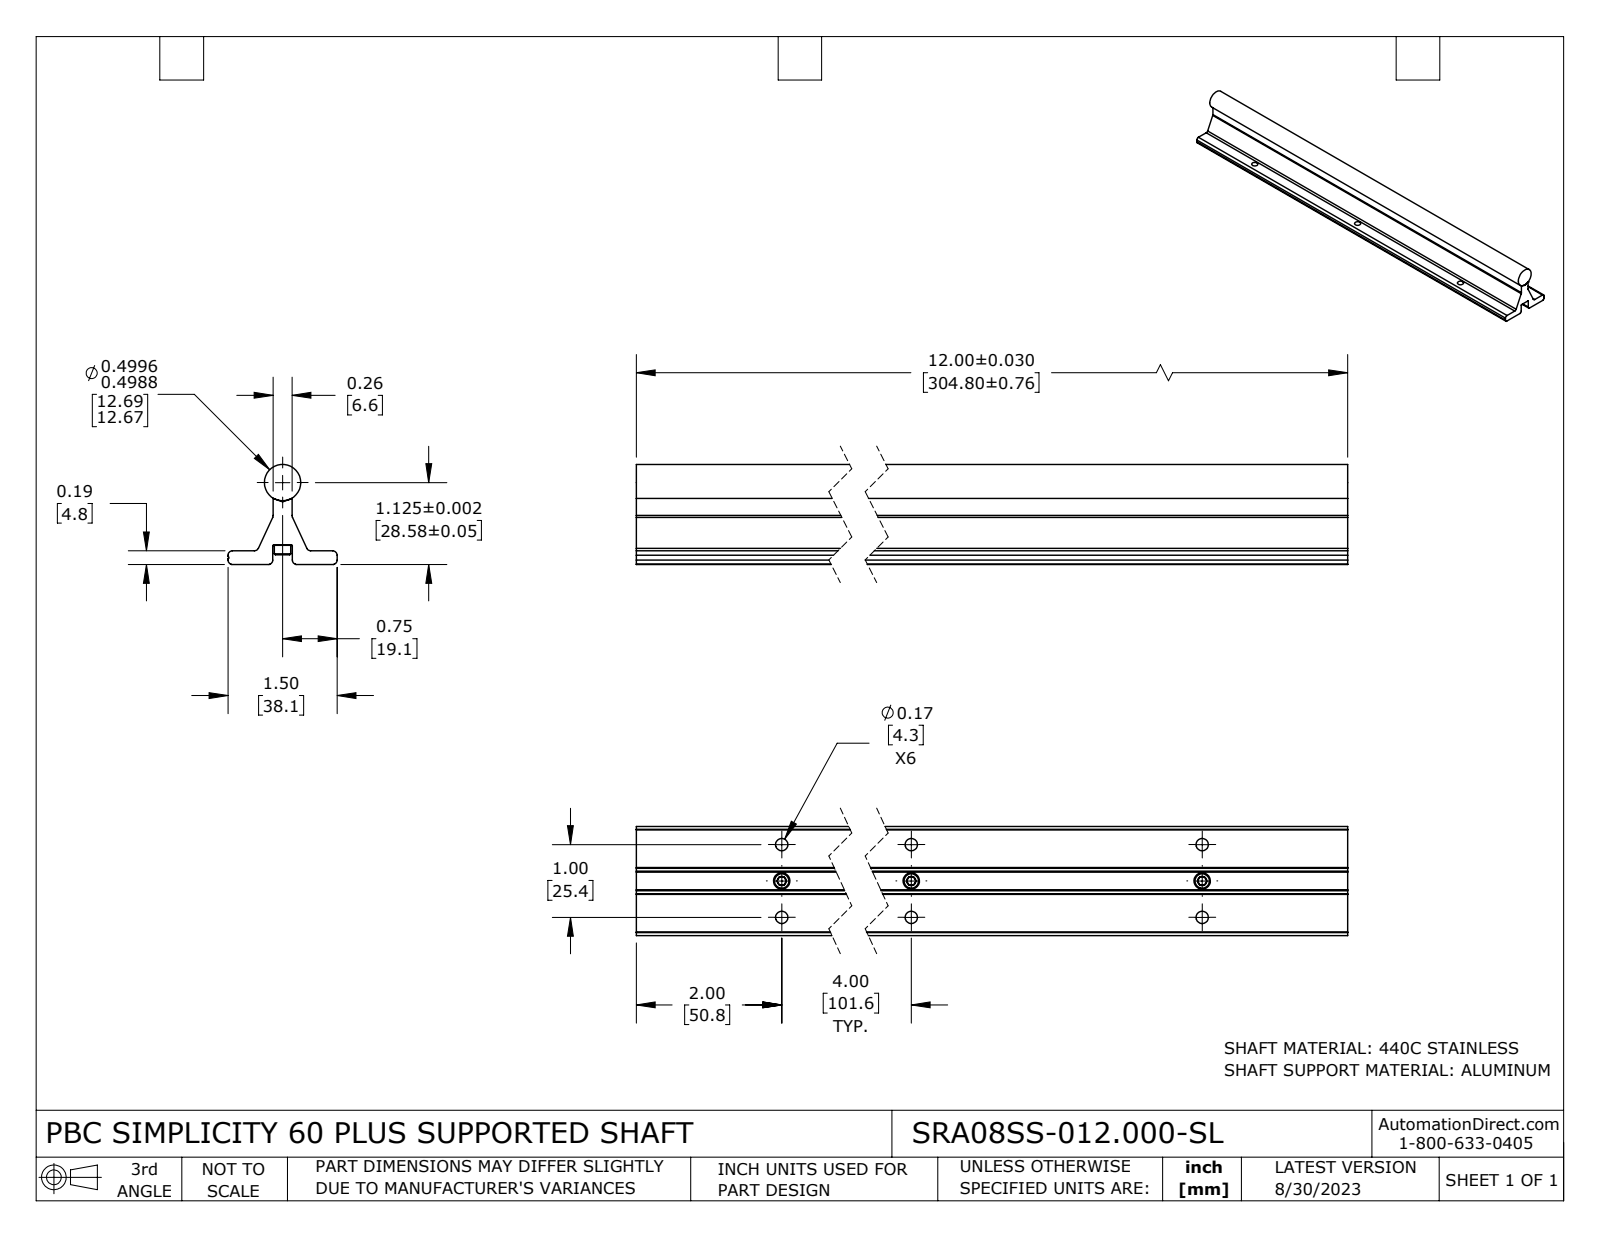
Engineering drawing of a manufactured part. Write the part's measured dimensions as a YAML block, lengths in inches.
part_name: "SRA08SS-012.000-SL"
step_written_by: "SolidWorks 2021 (CONFIG_CONTROL_DESIGN)"
units: inches
bodies: {solids: 5, faces: 161, planar: 60, cylindrical: 56, other: 45}
overall_size: [12, 1.5, 1.375]
volume: 8.191
surface_area: 81.83
round_holes:
  - {diameter: 0.17, count: 9}
  - {diameter: 0.116, count: 3}
  - {diameter: 0.156, count: 3}
round_bosses_or_shafts:
  - {diameter: 0.226, count: 3}
  - {diameter: 0.138, count: 3}
  - {diameter: 0.5, count: 1}
partial_cylinders:
  - {radius: 0.06, count: 8}
  - {radius: 0.015, count: 2}
  - {radius: 0.062, count: 1}
  - {radius: 0.063, count: 1}
face_to_face_distances: [0.187, 0.27, 0.265, 0.083, 0.26, 0.615, 0.62, 0.88, 0.885, 12]
hole_center_spacings: [4.031, 0.5, 4, 4.123, 8.016, 1, 8, 8.062]
